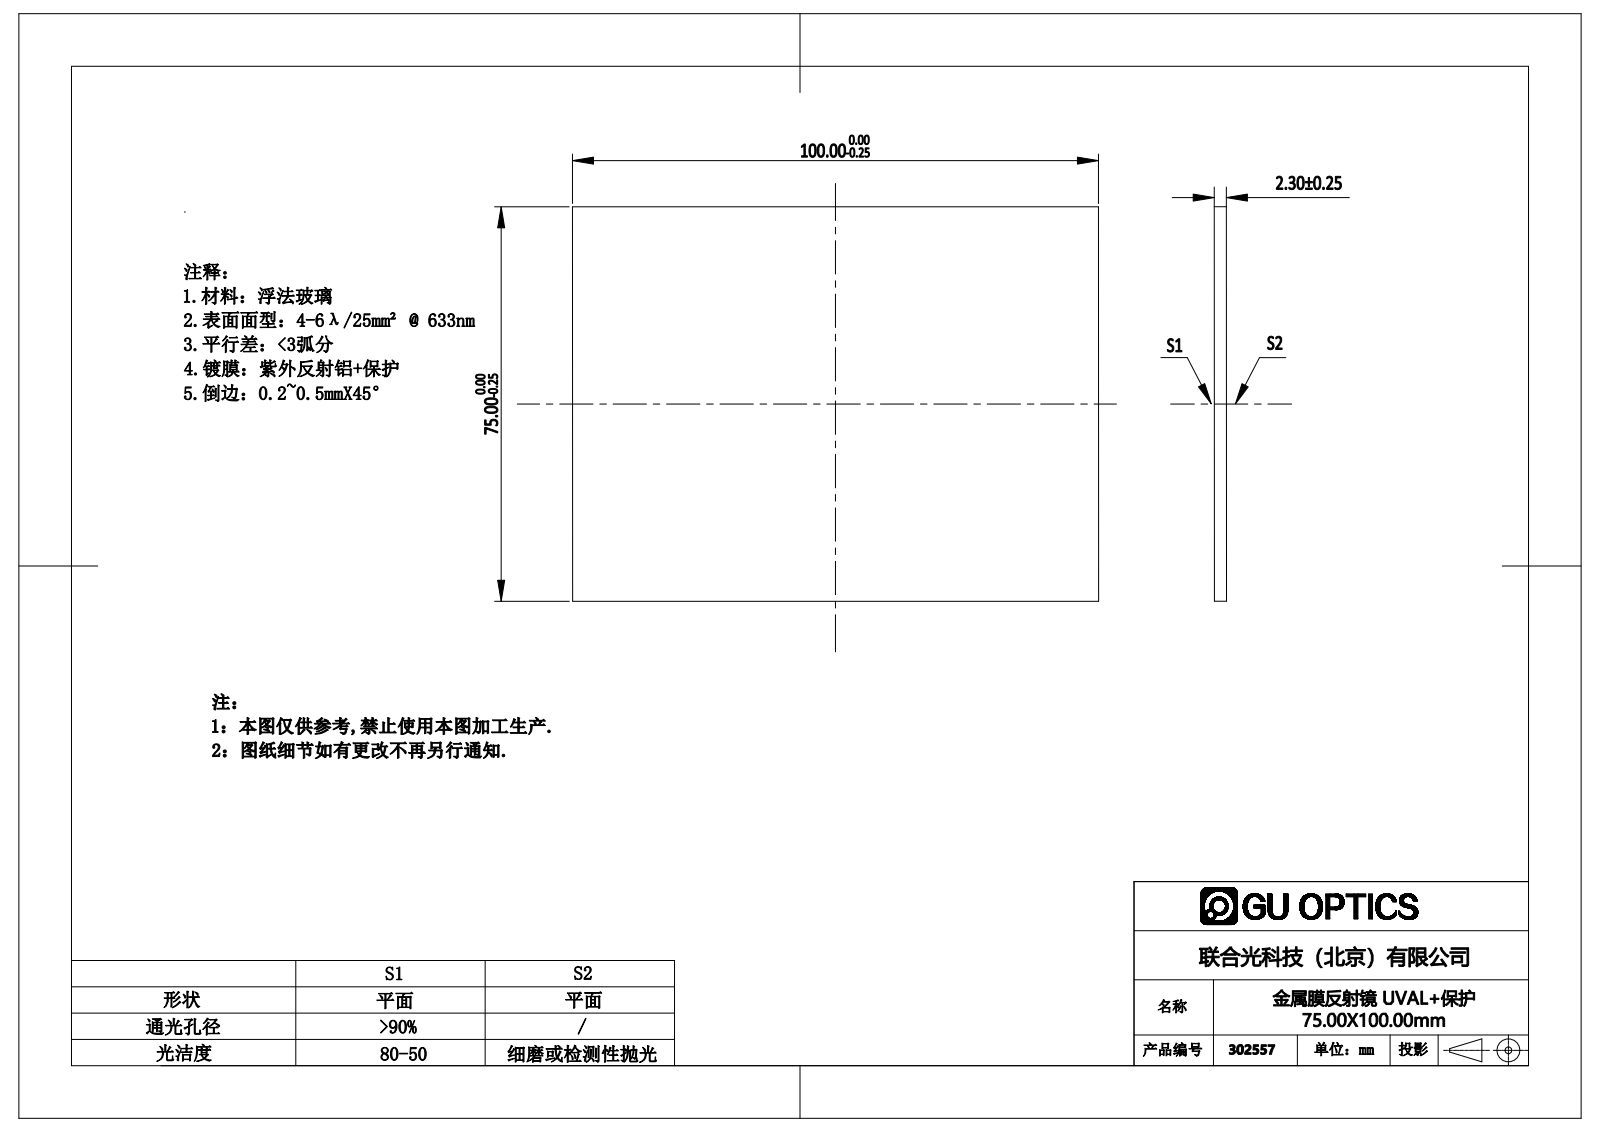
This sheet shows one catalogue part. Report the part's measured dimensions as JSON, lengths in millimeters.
{"part_name": "302528", "step_written_by": "SolidWorks 2016 (AUTOMOTIVE_DESIGN)", "units": "millimeters", "bodies": {"solids": 1, "faces": 6, "planar": 6, "cylindrical": 0, "other": 0}, "overall_size": [100.03, 75, 2.3], "volume_mm3": 17250, "surface_area_mm2": 15805, "face_to_face_distances": [2.3, 75, 100]}
